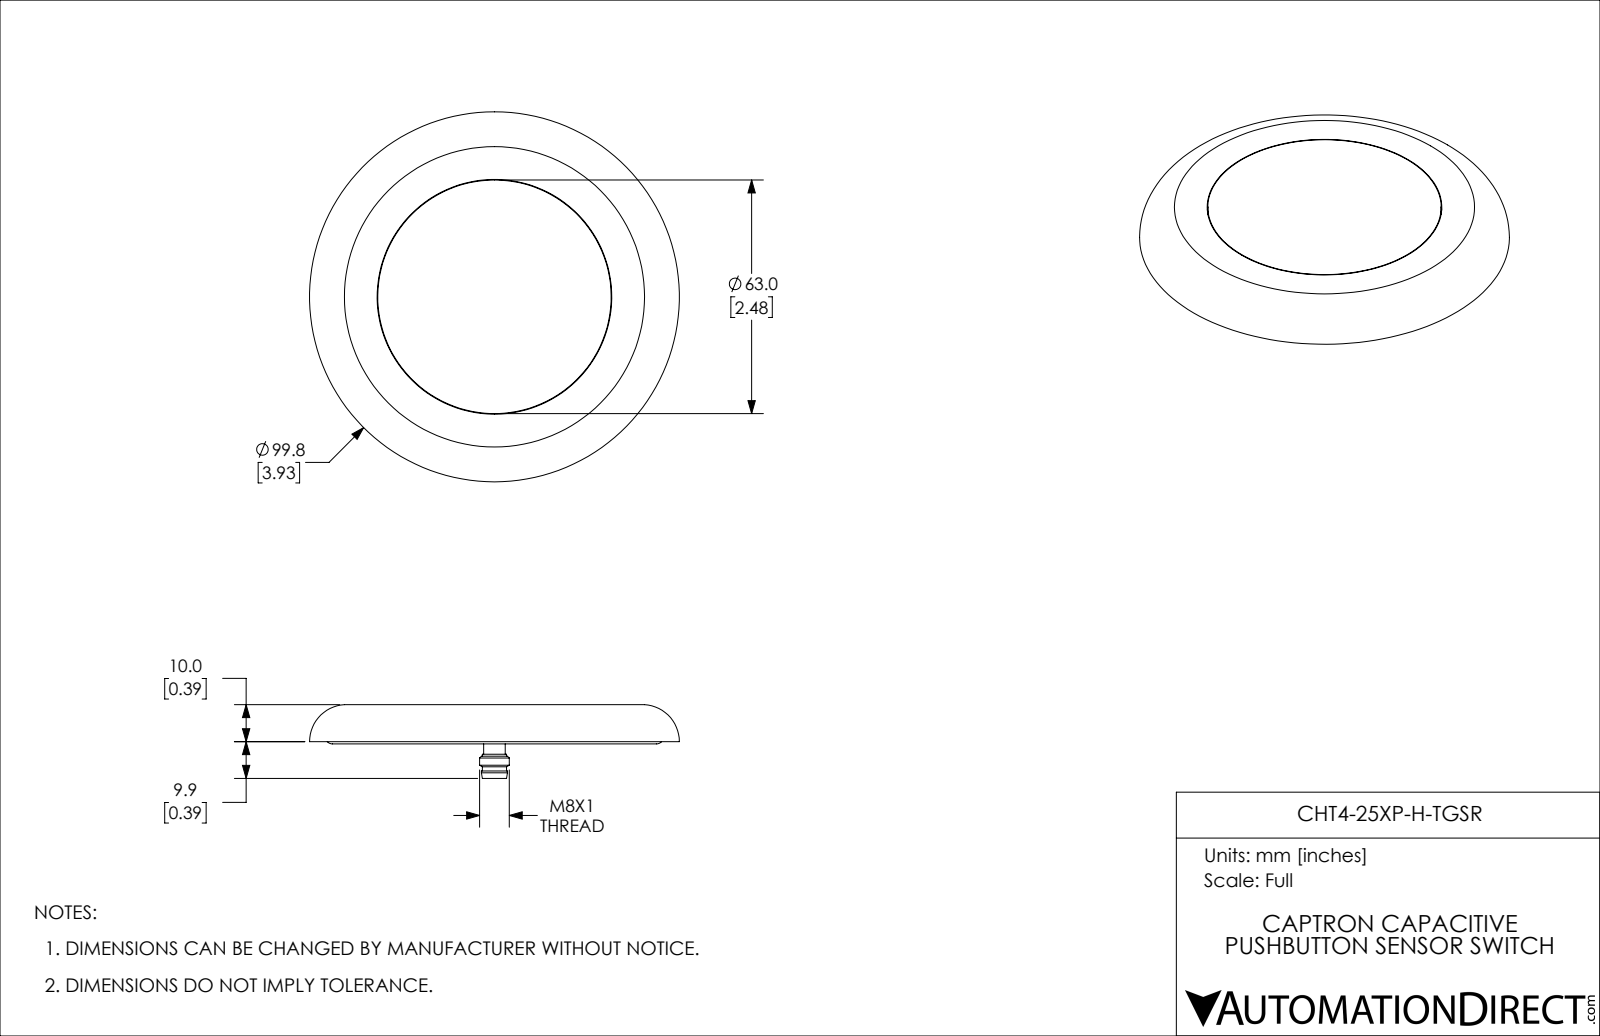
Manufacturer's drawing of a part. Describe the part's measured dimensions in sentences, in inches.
The part is named "CHT4-25XP-H-TGSR". Its 3-D file was written by "SolidWorks 2019 (CONFIG_CONTROL_DESIGN)". It is 13 solids with 102 faces: 30 planar, 32 cylindrical and 40 other. Overall it measures 3.929 by 3.929 by 0.783 inches. Its volume is 1.751 cubic inches and its surface area 63.84 square inches. Round holes: 1 of diameter 0.236, 1 of diameter 2.299, 1 of diameter 2.493, 1 of diameter 2.543. Round bosses or shafts: 4 of diameter 0.039, 1 of diameter 2.48, 1 of diameter 0.315, 1 of diameter 0.276, 1 of diameter 0.256, 1 of diameter 0.228. Partial cylindrical surfaces (rounded edges, fillets, slot ends): 1 of radius 1.26. The main face-to-face distances are 0.326, 0.056, 0.382, 0.057, 0.324, 0.269, 0.057, 0.39, 0.064, 0.332. The hole center spacings are 0.126.
